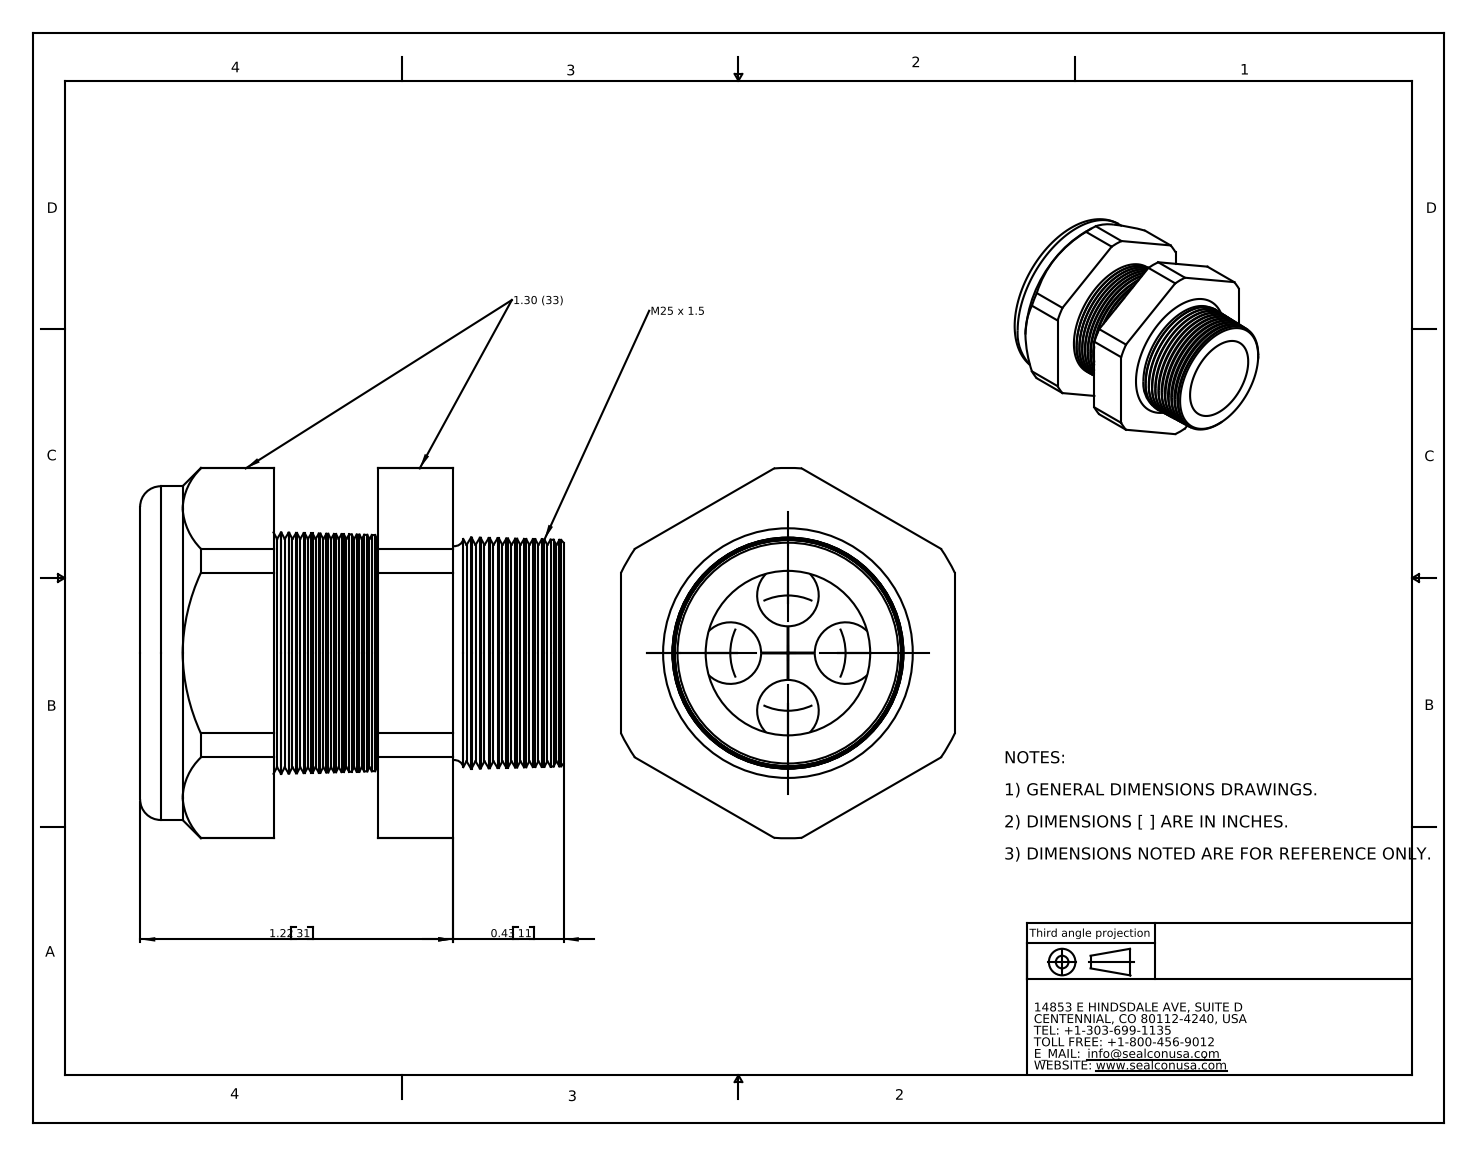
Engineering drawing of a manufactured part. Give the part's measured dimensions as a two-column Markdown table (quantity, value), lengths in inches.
| quantity | value |
| --- | --- |
| part name | CD25M1-BK |
| STEP written by | SolidWorks 2007 (CONFIG_CONTROL_DESIGN) |
| units | inches |
| bodies | 2 solids, 214 faces (20 planar, 28 cylindrical, 166 other) |
| overall size | 1.65 × 1.443 × 1.3 |
| volume | 1.131 in³ |
| surface area | 17.19 in² |
| round holes (diameter × count) | 0.24 × 4, 0.69 × 1, 0.71 × 1 |
| round bosses / shafts (diameter × count) | 1.3 × 1 |
| partial cylindrical surfaces (radius × count) | 0.721 × 1 |
| main face-to-face distances | 1.3, 0.405, 0.7, 0.295, 0.52, 0.925, 1.22, 1.65, 1.13, 0.725 |
| hole center spacings | 0.224, 0.317, 0.449 |
